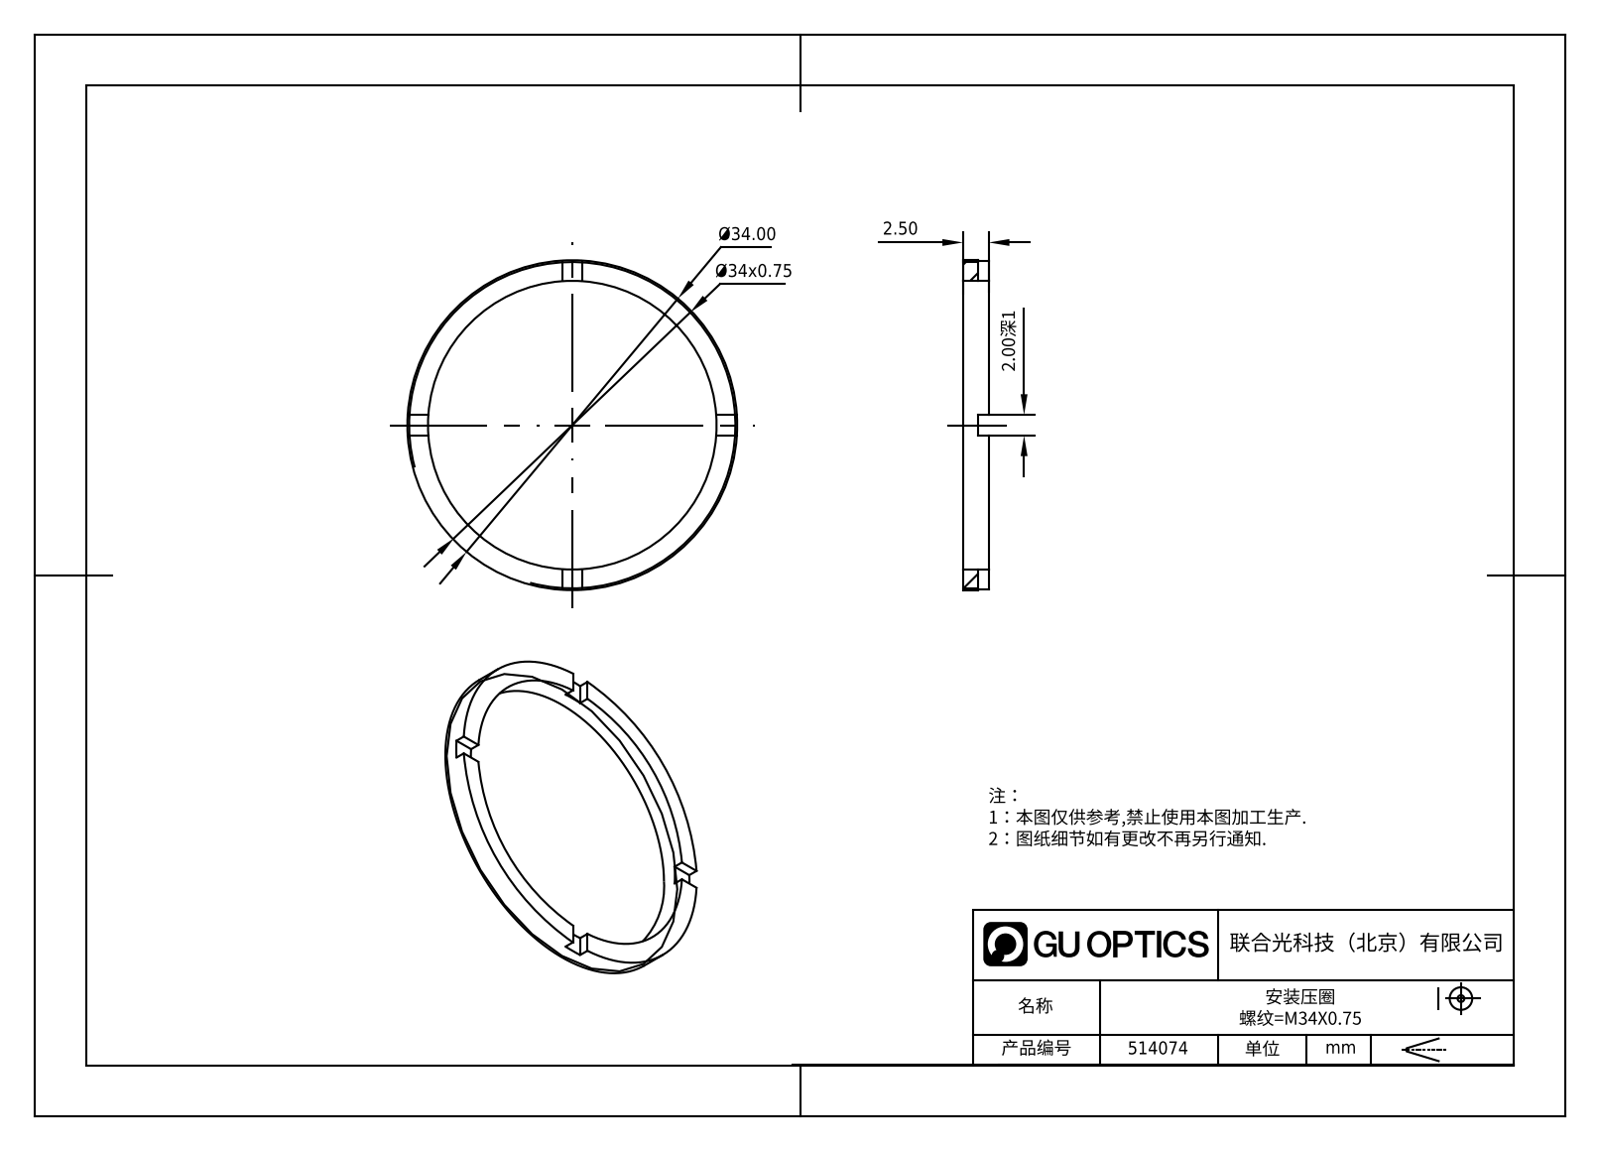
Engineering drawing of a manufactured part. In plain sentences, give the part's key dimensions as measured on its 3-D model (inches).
The part is named "514074". Its 3-D file was written by "SolidWorks 2020 (CONFIG_CONTROL_DESIGN)". It is 1 solid with 21 faces: 17 planar, 4 cylindrical and 0 other. Overall it measures 1.339 by 1.339 by 0.098 inches. Its volume is 0.03 cubic inches and its surface area 1.4 square inches. Round holes: 1 of diameter 1.181. Round bosses or shafts: 1 of diameter 1.339. The main face-to-face distances are 0.098, 0.059, 0.039, 0.079.
